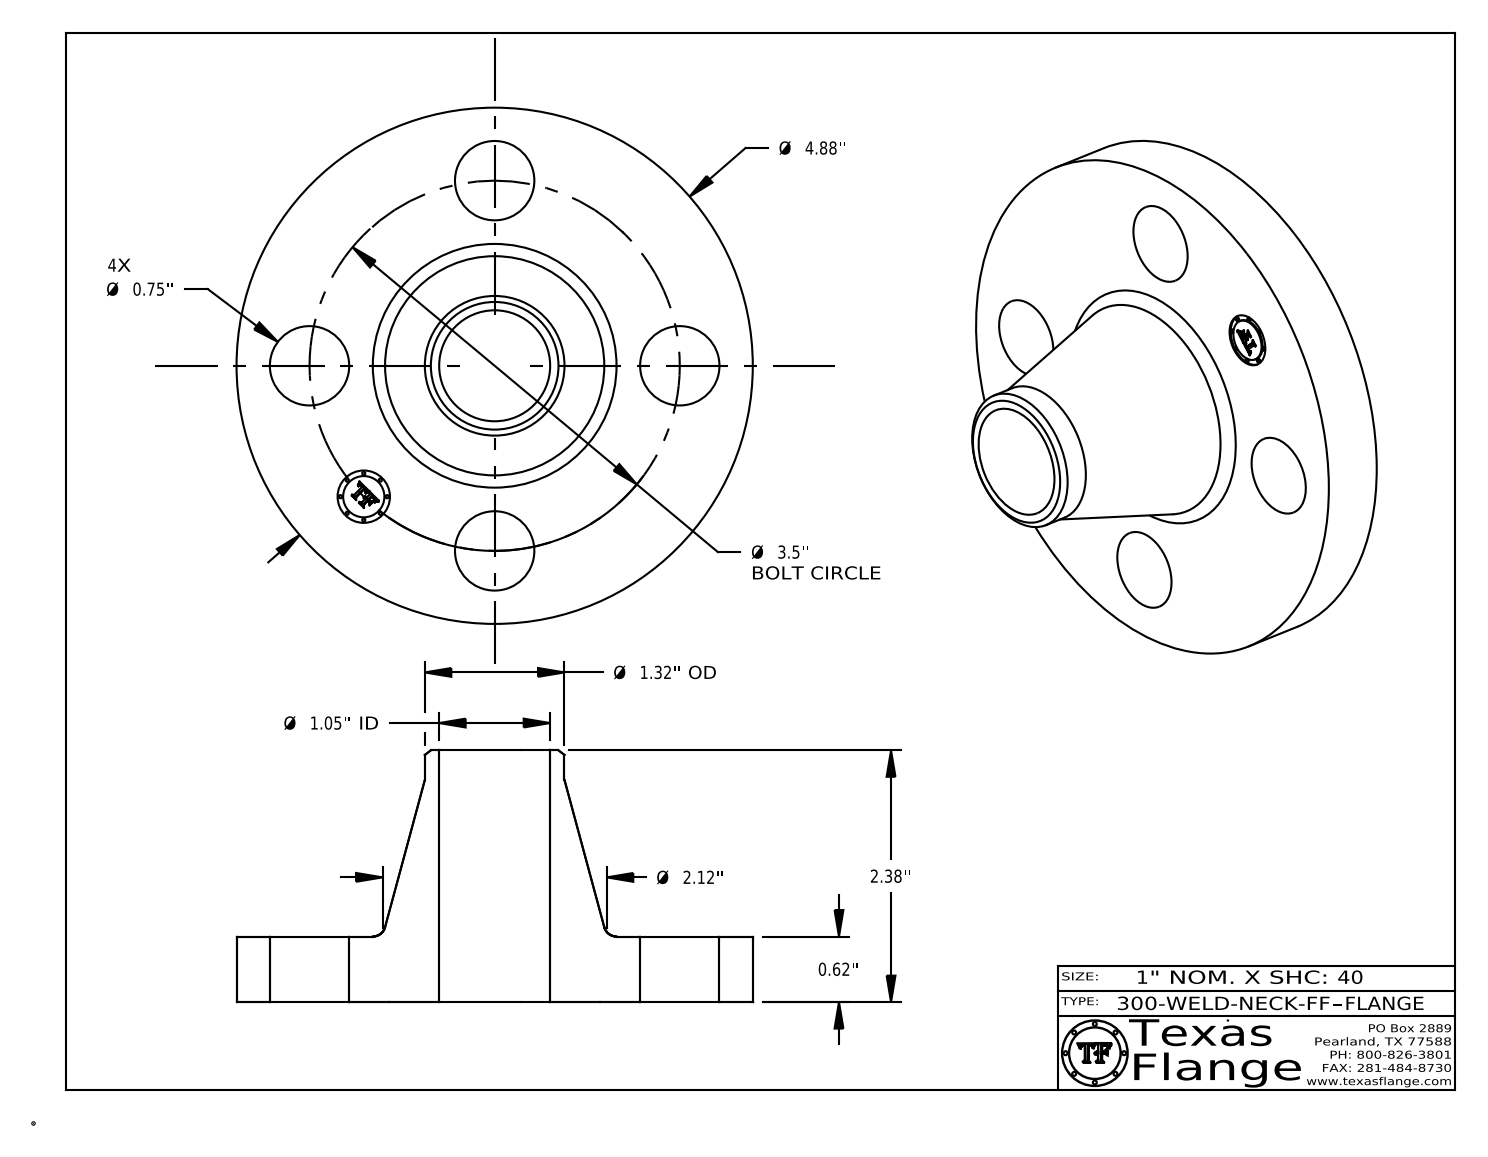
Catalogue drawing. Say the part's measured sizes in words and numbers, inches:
The part is named "300-WELD-NECK-FF". Its 3-D file was written by "CATIA V5 STEP AP214 (AUTOMOTIVE_DESIGN)". It is 1 solid with 409 faces: 369 planar, 34 cylindrical and 6 other. Overall it measures 4.88 by 4.88 by 2.38 inches. Its volume is 12.33 cubic inches and its surface area 62.42 square inches. Round holes: 4 of diameter 0.75, 1 of diameter 0.495, 1 of diameter 1.049. Round bosses or shafts: 8 of diameter 0.03, 1 of diameter 4.88, 1 of diameter 1.32, 1 of diameter 0.39. The main face-to-face distances are 0.62, 2.38, 1.76, 0.015, 0.605, 1.775, 0.148, 0.145, 0.027, 0.096. The hole center spacings are 1.75, 2.475, 1.339, 3.233, 3.5.
